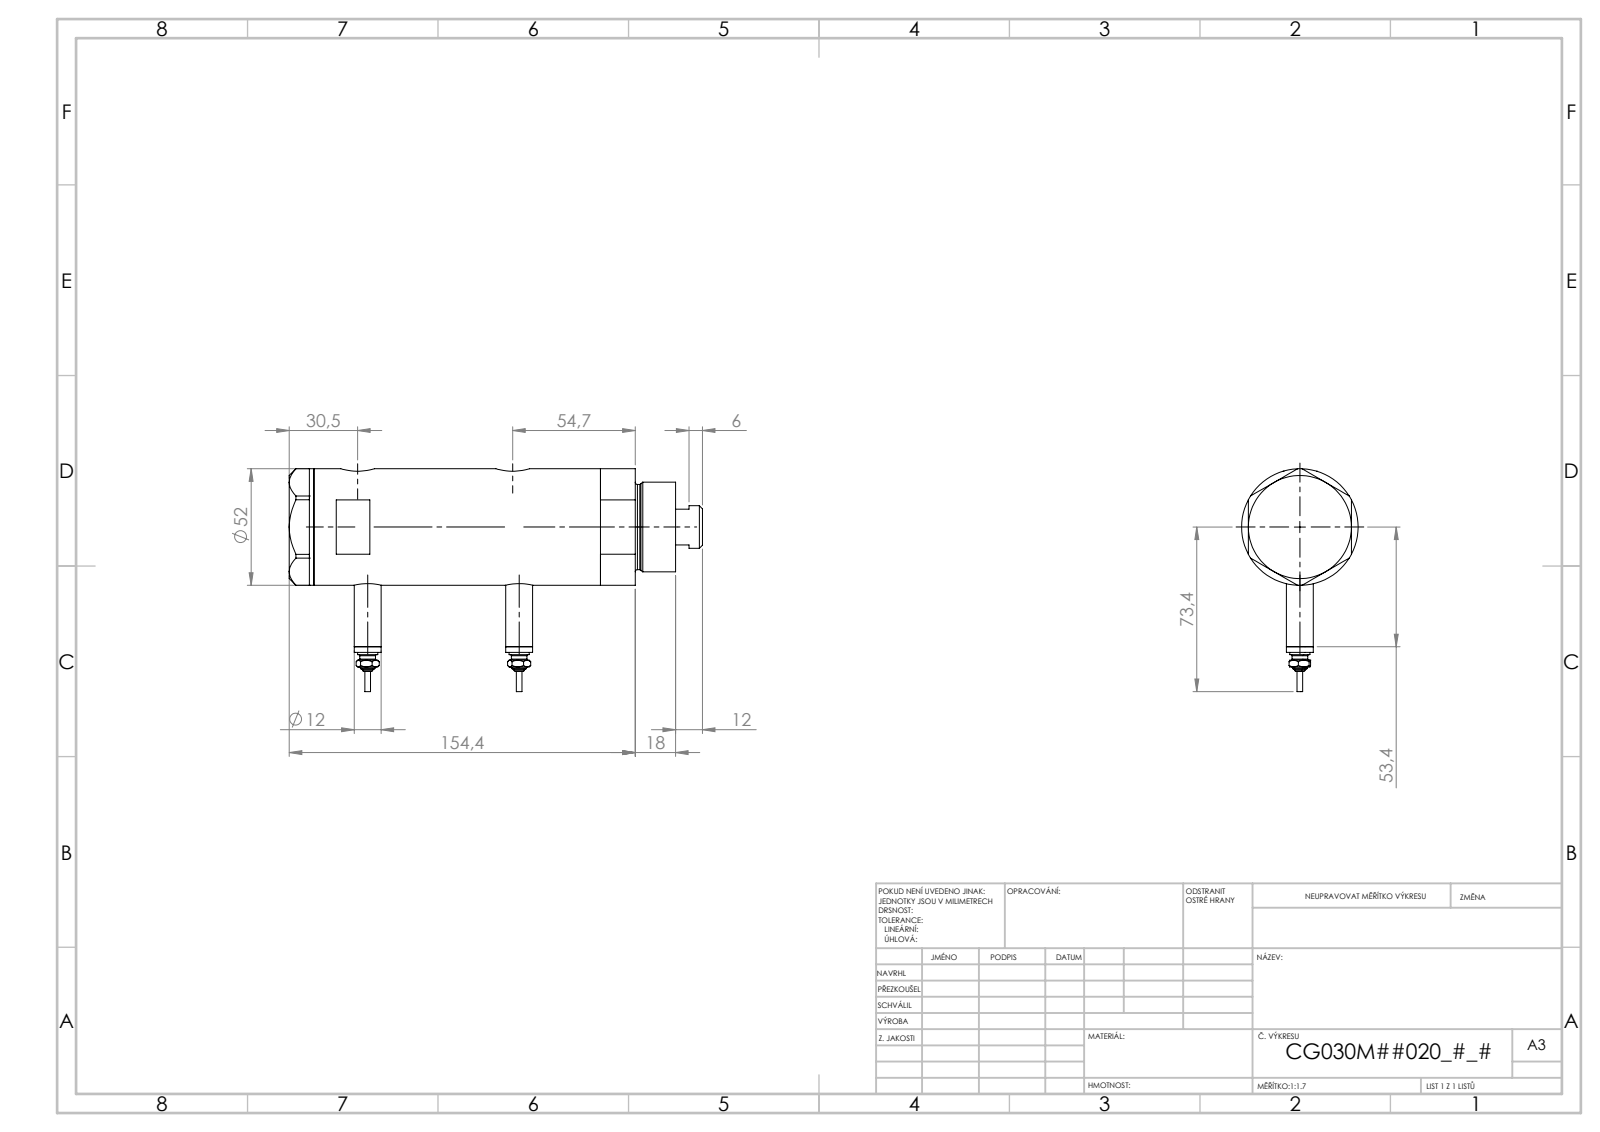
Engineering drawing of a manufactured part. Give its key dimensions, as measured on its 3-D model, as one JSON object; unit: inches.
{"part_name": "V270CG_MIDDLE; V270CG_FRONT; V270CG_VC; V270CG_BACK (+1 more)", "step_written_by": "SolidWorks 2019 (CONFIG_CONTROL_DESIGN)", "units": "inches", "bodies": {"solids": 6, "faces": 226, "planar": 93, "cylindrical": 69, "other": 64}, "overall_size": [7.26, 3.913, 2.047], "volume_in3": 21.04, "surface_area_in2": 124.4, "round_holes": [[0.383, 2], [0.492, 2], [0.591, 2], [0.256, 1], [0.787, 1], [0.846, 1], [1.181, 1], [1.299, 1], [1.732, 1]], "round_bosses_or_shafts": [[0.472, 2], [0.354, 2], [0.276, 2], [0.177, 2], [0.098, 2], [2.047, 1], [1.575, 1], [1.496, 1]], "face_to_face_distances": [3.602, 0.937, 2.665, 0.433, 1.37, 4.035, 1.811, 1.433, 5.469, 5.035], "hole_center_spacings": [0.114, 0.177, 2.547, 2.661, 2.724, 2.839]}
